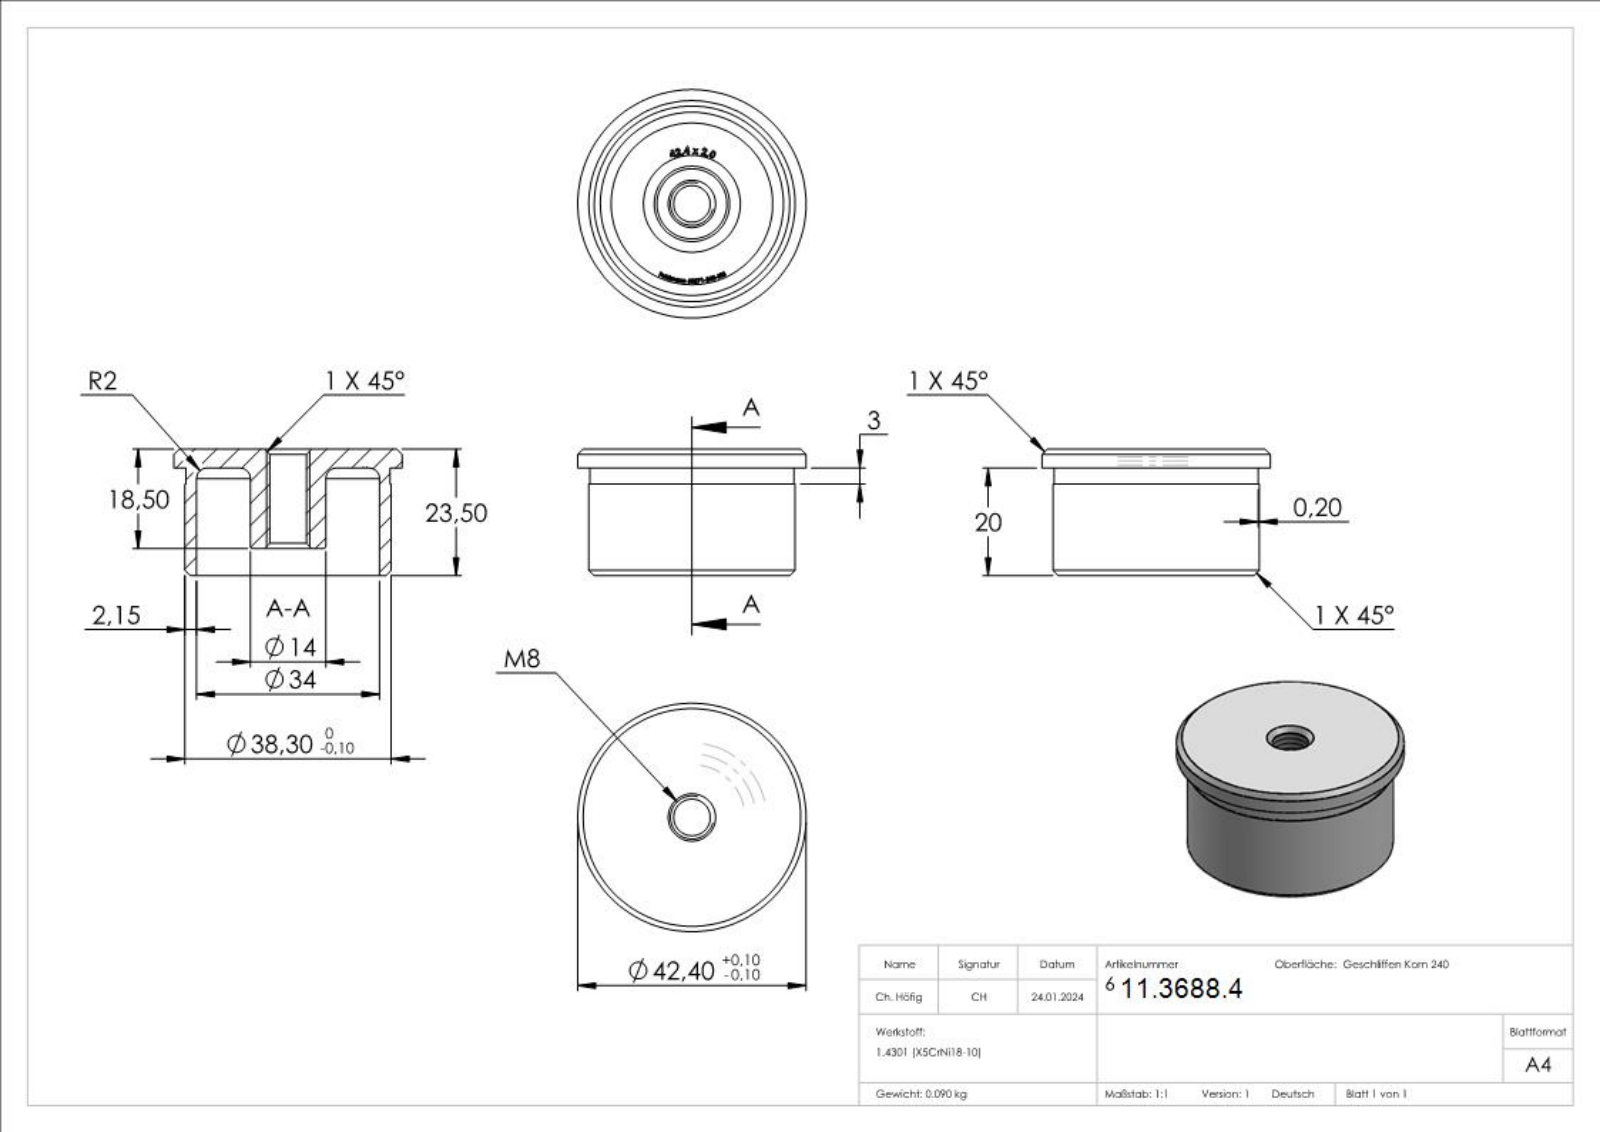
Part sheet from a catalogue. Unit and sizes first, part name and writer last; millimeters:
Units: millimetres
Overall size (bounding box): 42.4 × 42.4 × 23.5
Round holes (diameter × count): ⌀6.8 ×1, ⌀34 ×1
Round bosses / shafts (diameter × count): ⌀42.4 ×1, ⌀38.3 ×1, ⌀37.9 ×1, ⌀14 ×1
Main face-to-face distances: 3.5, 20, 23.5, 5, 15, 18.5, 17, 12, 3, 6.5
Volume: 11 369 mm³ · Surface area: 8 557 mm²
Bodies: 1 solid, 364 faces (228 planar, 6 cylindrical, 130 other)
Part name (STEP PRODUCT): 60271-240-M8
STEP written by: SolidWorks 2018 (CONFIG_CONTROL_DESIGN)
